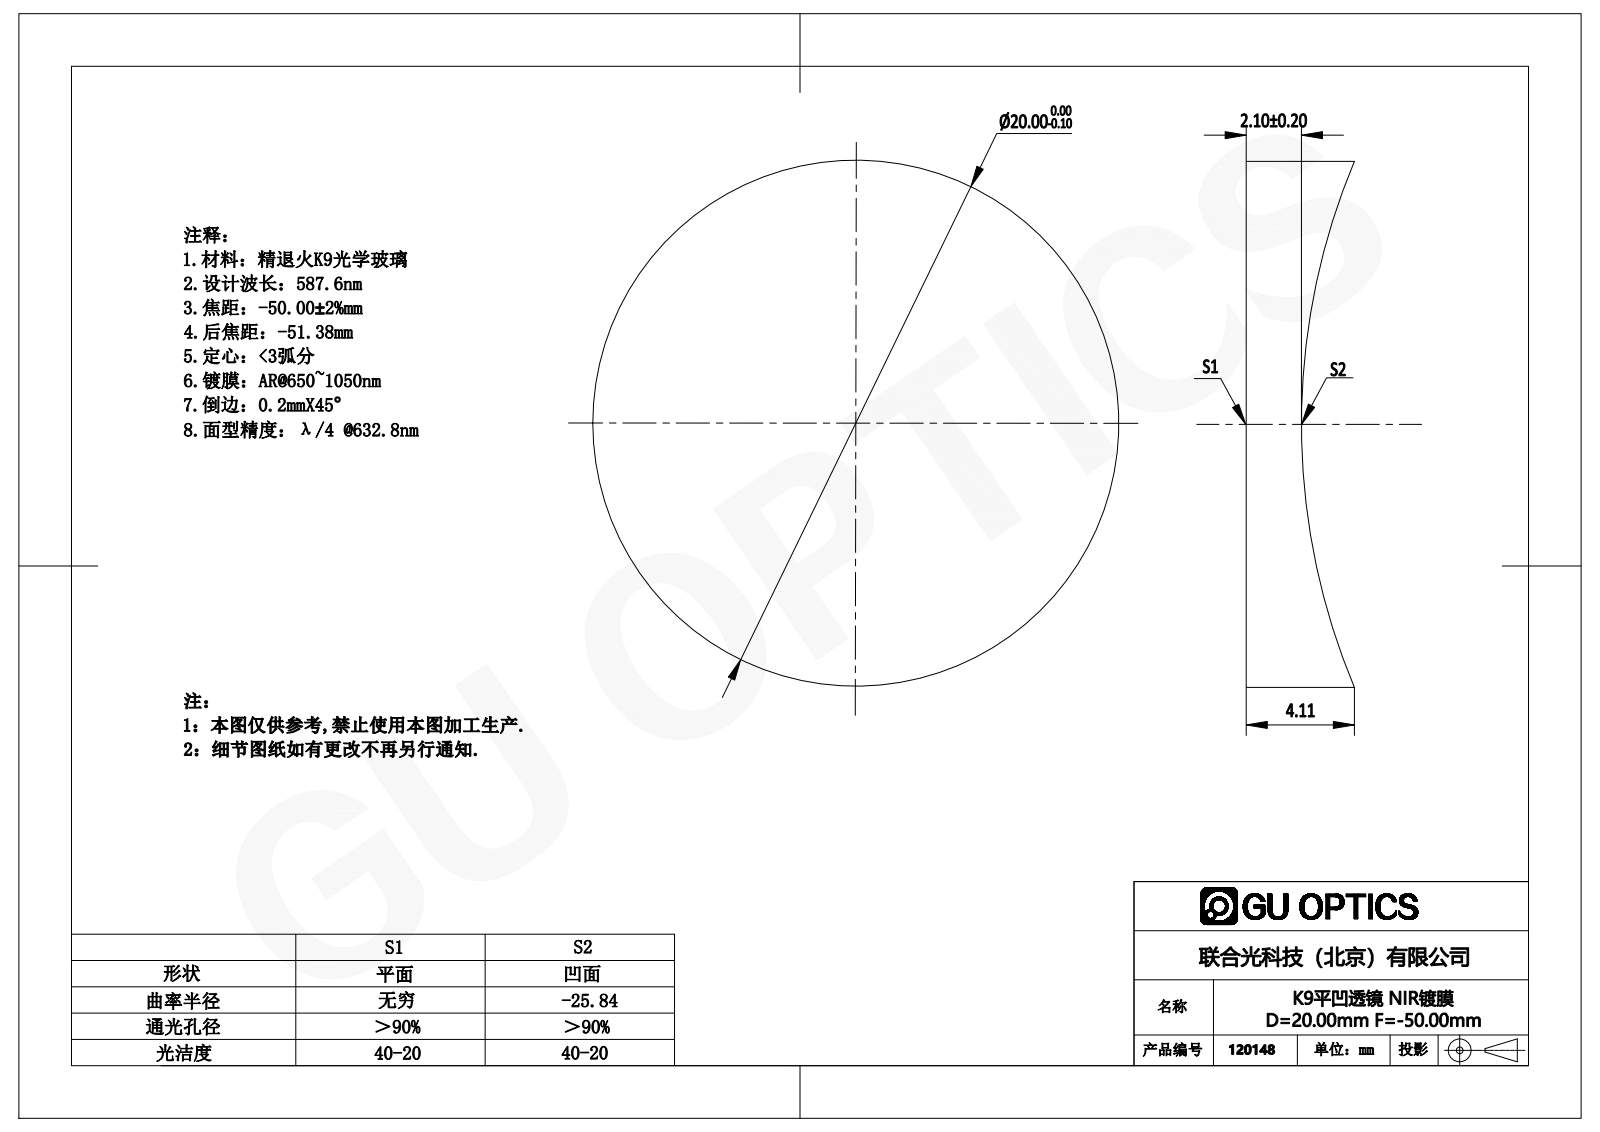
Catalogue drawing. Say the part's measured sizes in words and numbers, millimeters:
The part is named "120148". Its 3-D file was written by "SolidWorks 2016 (AUTOMOTIVE_DESIGN)". It is 1 solid with 5 faces: 1 planar, 2 cylindrical and 2 other. Overall it measures 20 by 20 by 4.11 millimeters. Its volume is 972 cubic millimeters and its surface area 900 square millimeters. Round bosses or shafts: 1 of diameter 20.
